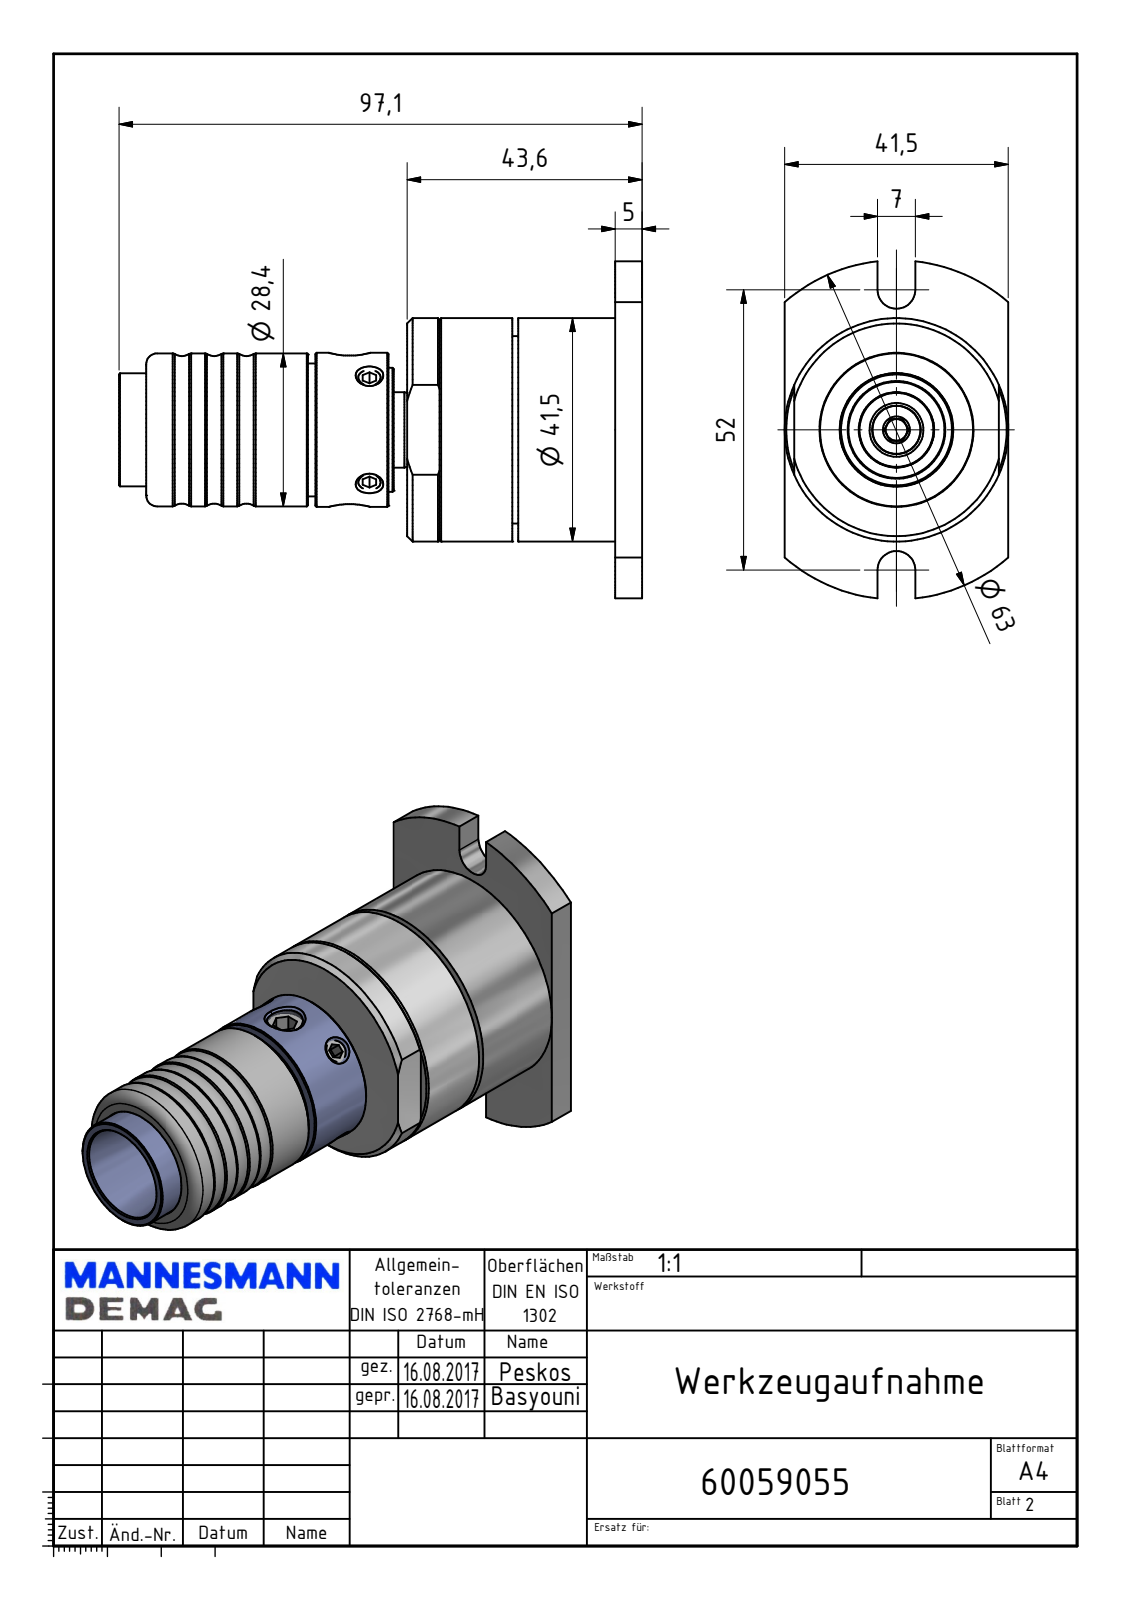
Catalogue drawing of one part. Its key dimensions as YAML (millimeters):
part_name: "60059055"
step_written_by: "Autodesk Inventor 2021 (AUTOMOTIVE_DESIGN)"
units: millimeters
bodies: {solids: 1, faces: 241, planar: 111, cylindrical: 74, other: 56}
overall_size: [97.1, 62.61, 41.5]
volume: 89629
surface_area: 19426
round_holes:
  - {diameter: 3.5, count: 2}
  - {diameter: 4.13, count: 2}
  - {diameter: 4, count: 1}
  - {diameter: 5.6, count: 1}
  - {diameter: 6.65, count: 1}
  - {diameter: 9, count: 1}
  - {diameter: 16, count: 1}
  - {diameter: 21.1, count: 1}
  - {diameter: 25, count: 1}
round_bosses_or_shafts:
  - {diameter: 41.5, count: 1}
  - {diameter: 34.79, count: 1}
  - {diameter: 28.6, count: 1}
  - {diameter: 28.4, count: 1}
  - {diameter: 24.7, count: 1}
  - {diameter: 23, count: 1}
  - {diameter: 21, count: 1}
  - {diameter: 14.95, count: 1}
partial_cylinders:
  - {radius: 2.5, count: 2}
  - {radius: 3.5, count: 2}
  - {radius: 6.58, count: 1}
  - {radius: 8.8, count: 1}
  - {radius: 31.5, count: 1}
face_to_face_distances: [43.6, 38.6, 5, 23, 24.1, 20.6, 18, 19.5, 1.1, 19.1]
